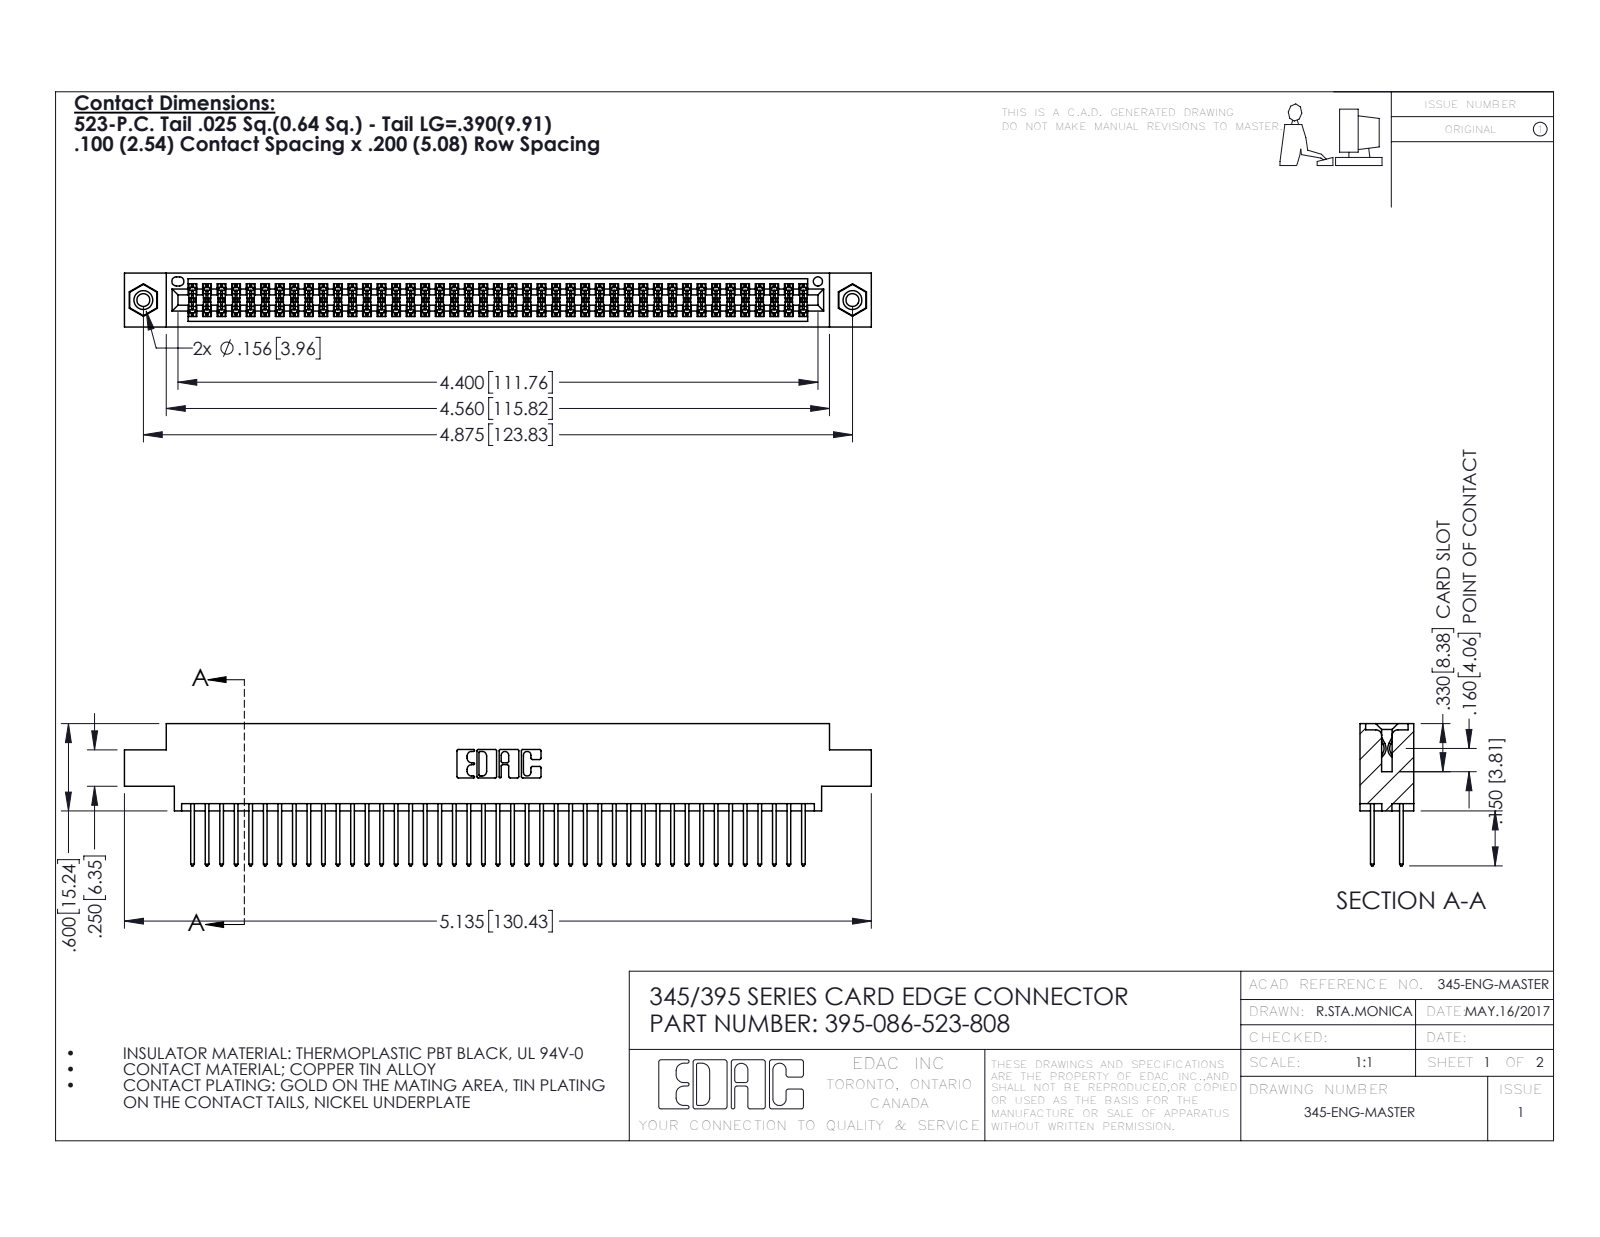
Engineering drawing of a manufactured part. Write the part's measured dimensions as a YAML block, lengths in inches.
part_name: "395-086-523-808; 345 Part_0.170 Offset - 0.156 Dia-TI; 345-250-001_345-250-003-102; 345-292-001_345-293-123"
step_written_by: "SolidWorks 2016 (CONFIG_CONTROL_DESIGN)"
units: inches
bodies: {solids: 89, faces: 4490, planar: 2954, cylindrical: 1520, other: 16}
overall_size: [5.135, 0.977, 0.37]
volume: 0.777
surface_area: 30.68
round_holes:
  - {diameter: 0.089, count: 2}
  - {diameter: 0.125, count: 2}
  - {diameter: 0.156, count: 2}
  - {diameter: 0.064, count: 1}
round_bosses_or_shafts:
  - {diameter: 0.155, count: 2}
partial_cylinders:
  - {radius: 0.006, count: 129}
  - {radius: 0.01, count: 86}
  - {radius: 0.01, count: 22}
  - {radius: 0.007, count: 6}
  - {radius: 0.031, count: 6}
  - {radius: 0.026, count: 3}
  - {radius: 0.014, count: 2}
  - {radius: 0.019, count: 2}
face_to_face_distances: [0.072, 0.298, 0.2, 0.098, 0.272, 0.025, 0.37, 0.225, 0.175, 0.149]
hole_center_spacings: [0.27, 4.639, 4.875]
